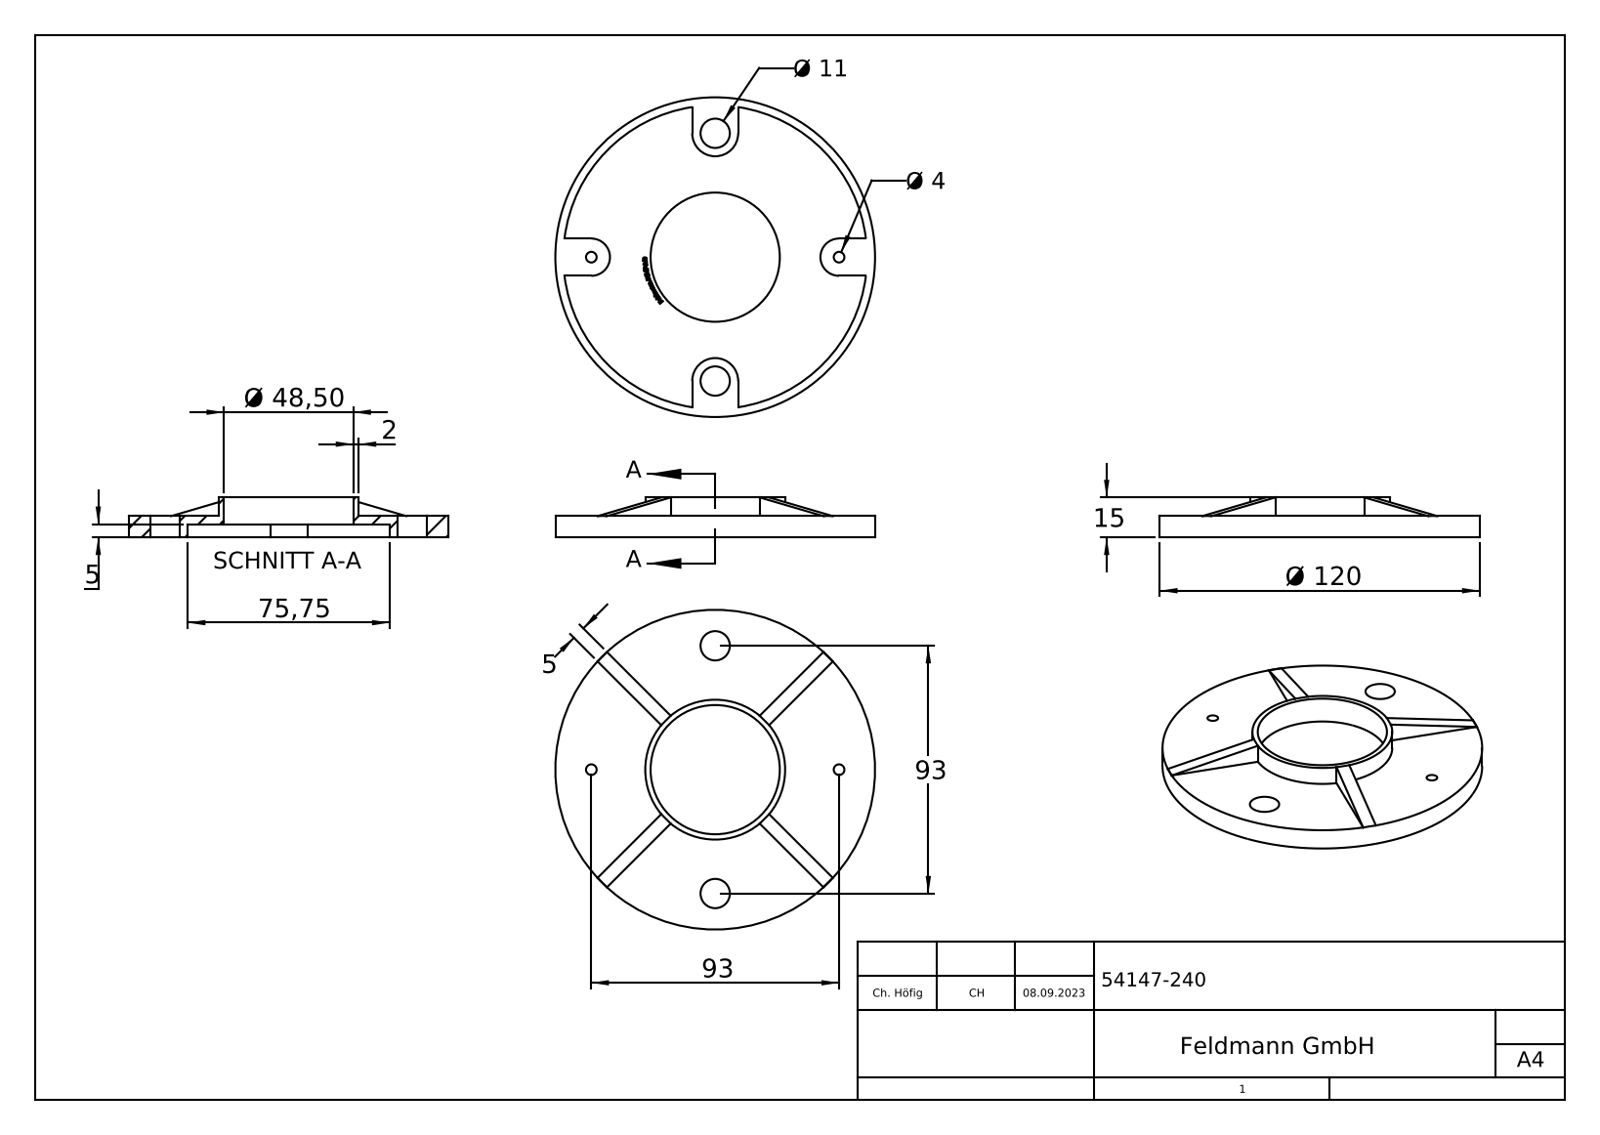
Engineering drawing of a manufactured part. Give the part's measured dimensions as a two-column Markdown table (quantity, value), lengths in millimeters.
| quantity | value |
| --- | --- |
| part name | 54147-240 |
| STEP written by | SolidWorks 2018 (CONFIG_CONTROL_DESIGN) |
| units | millimeters |
| bodies | 1 solid, 265 faces (176 planar, 18 cylindrical, 71 other) |
| overall size | 120 × 120 × 15 |
| volume | 41 917 mm³ |
| surface area | 28 140 mm² |
| round holes (diameter × count) | 4 × 2, 11 × 2, 48.5 × 1, 114 × 1 |
| round bosses / shafts (diameter × count) | 120 × 1, 52.5 × 1 |
| partial cylindrical surfaces (radius × count) | 7 × 2, 8.62 × 2 |
| main face-to-face distances | 3, 5, 8, 15, 10, 7, 14, 17.25, 17.26, 5.1 |
| hole center spacings | 46.5, 65.76, 93 |
